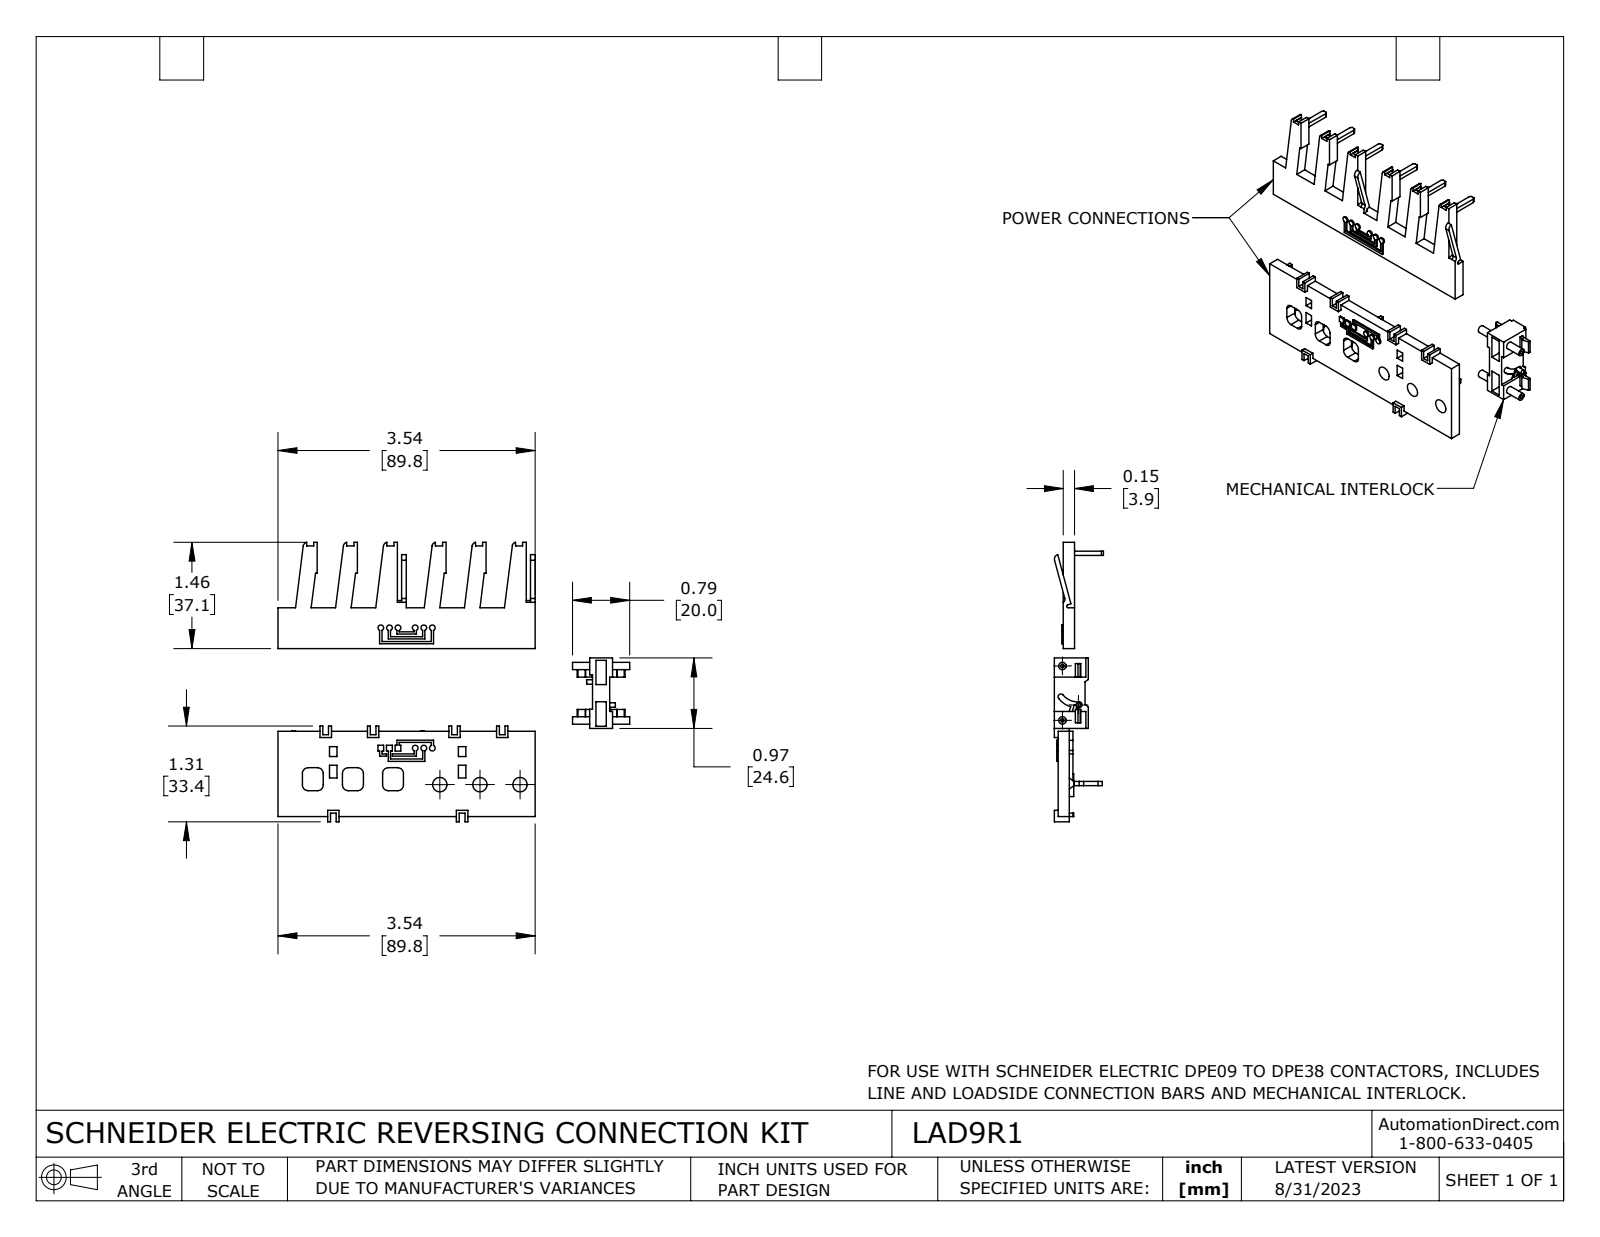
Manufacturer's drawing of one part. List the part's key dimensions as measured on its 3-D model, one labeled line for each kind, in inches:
Part name (STEP PRODUCT): LAD9R1
STEP written by: SolidWorks 2021 (CONFIG_CONTROL_DESIGN)
Units: inches
Bodies: 9 solids, 801 faces (694 planar, 107 cylindrical, 0 other)
Overall size (bounding box): 4.835 × 3.842 × 0.673
Volume: 1.215 in³ · Surface area: 26.73 in²
Round holes (diameter × count): ⌀0.197 ×3, ⌀0.047 ×2
Round bosses / shafts (diameter × count): ⌀0.079 ×9, ⌀0.102 ×2, ⌀0.06 ×2
Partial cylindrical surfaces — rounded edges, fillets, slot ends (radius × count): R0.079 ×12, R0.008 ×6, R0.059 ×6, R0.016 ×4, R0.039 ×4, R0.02 ×2, R0.256 ×2, R0.335 ×2
Main face-to-face distances: 0.154, 0.071, 0.083, 0.224, 0.047, 0.051, 0.205, 0.276, 0.02, 0.087
Hole centre spacings: 0.551, 0.748, 1.102
